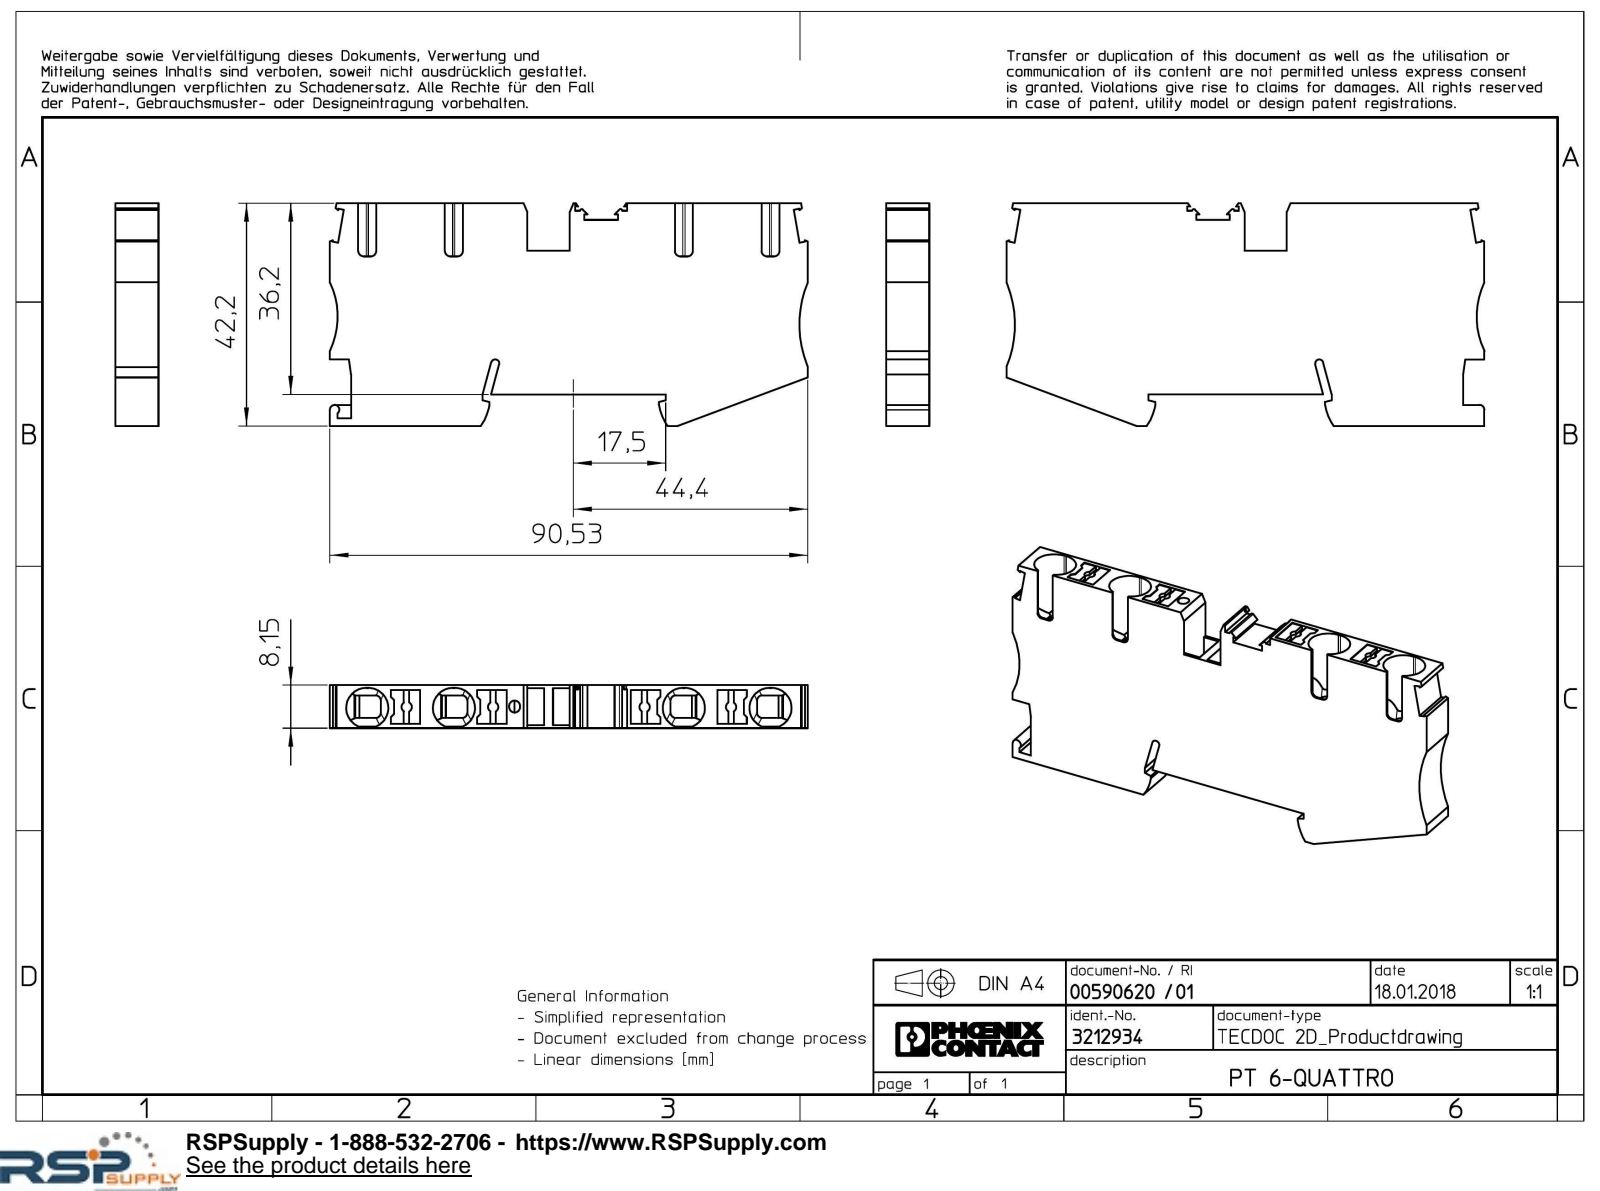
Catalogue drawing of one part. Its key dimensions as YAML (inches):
part_name: "PT_6_QUATTRO-select"
step_written_by: "Creo Elements/Direct Modeling 20.1A 29-Sep-2018 (C) Parametric Technology GmbH (AUTOMOTIVE_DESIGN)"
units: inches
bodies: {solids: 1, faces: 258, planar: 202, cylindrical: 56, other: 0}
overall_size: [3.564, 1.661, 0.321]
volume: 1.395
surface_area: 18.2
partial_cylinders:
  - {radius: 0.039, count: 28}
  - {radius: 0.15, count: 8}
  - {radius: 0.118, count: 4}
  - {radius: 0.012, count: 2}
  - {radius: 0.041, count: 2}
  - {radius: 0.374, count: 2}
  - {radius: 0.028, count: 1}
  - {radius: 0.031, count: 1}
face_to_face_distances: [0.321, 0.236, 1.661, 1.425, 0.124, 0.191, 0.315, 0.077, 0.244, 0.246]
